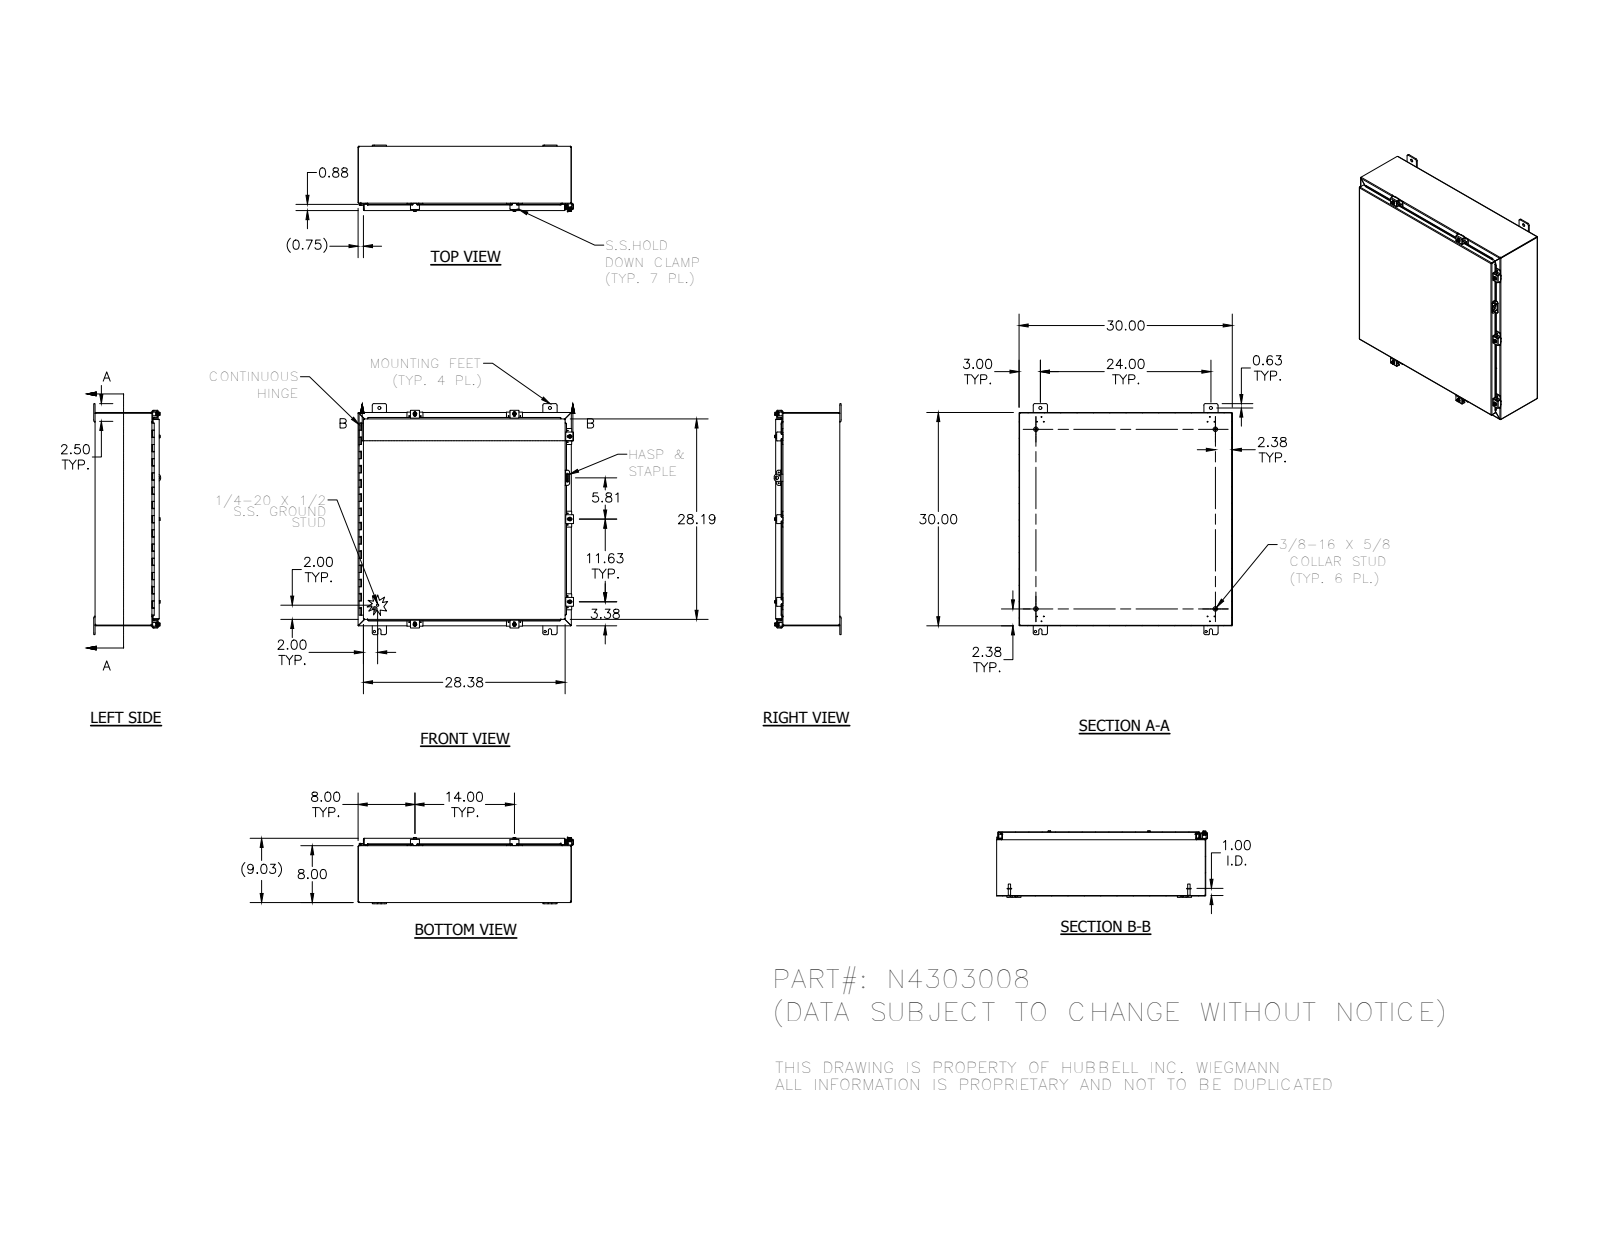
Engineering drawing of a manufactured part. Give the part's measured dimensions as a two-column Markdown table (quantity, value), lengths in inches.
| quantity | value |
| --- | --- |
| part name | N43030LID_1; 38846_1; 30824_1; 28x28_1 (+8 more) |
| STEP written by | SolidWorks 2014 (AUTOMOTIVE_DESIGN) |
| units | inches |
| bodies | 52 solids, 2311 faces (889 planar, 1039 cylindrical, 383 other) |
| overall size | 32.5 × 30.311 × 9.41 |
| volume | 246 in³ |
| surface area | 6 454 in² |
| round holes (diameter × count) | 0.11 × 17, 0.12 × 12, 0.211 × 7, 0.281 × 7, 0.3 × 7, 0.313 × 4, 0.438 × 4, 0.125 × 1, 0.156 × 1, 0.5 × 1 |
| round bosses / shafts (diameter × count) | 0.25 × 9, 0.52 × 7, 0.5 × 7, 0.35 × 7, 0.625 × 4, 0.33 × 4, 0.115 × 2, 0.337 × 1 |
| partial cylindrical surfaces (radius × count) | 0.03 × 83, 0.062 × 41, 0.125 × 37, 0.25 × 33, 0.031 × 23, 0.105 × 23, 0.063 × 14, 0.141 × 14 |
| main face-to-face distances | 0.074, 8.959, 29.926, 8.885, 9.033, 29.852, 30, 7.926, 1.033, 8 |
| hole center spacings | 24, 0.876, 0.759, 0.94, 0.969, 1.995, 23.367, 24.335 |
